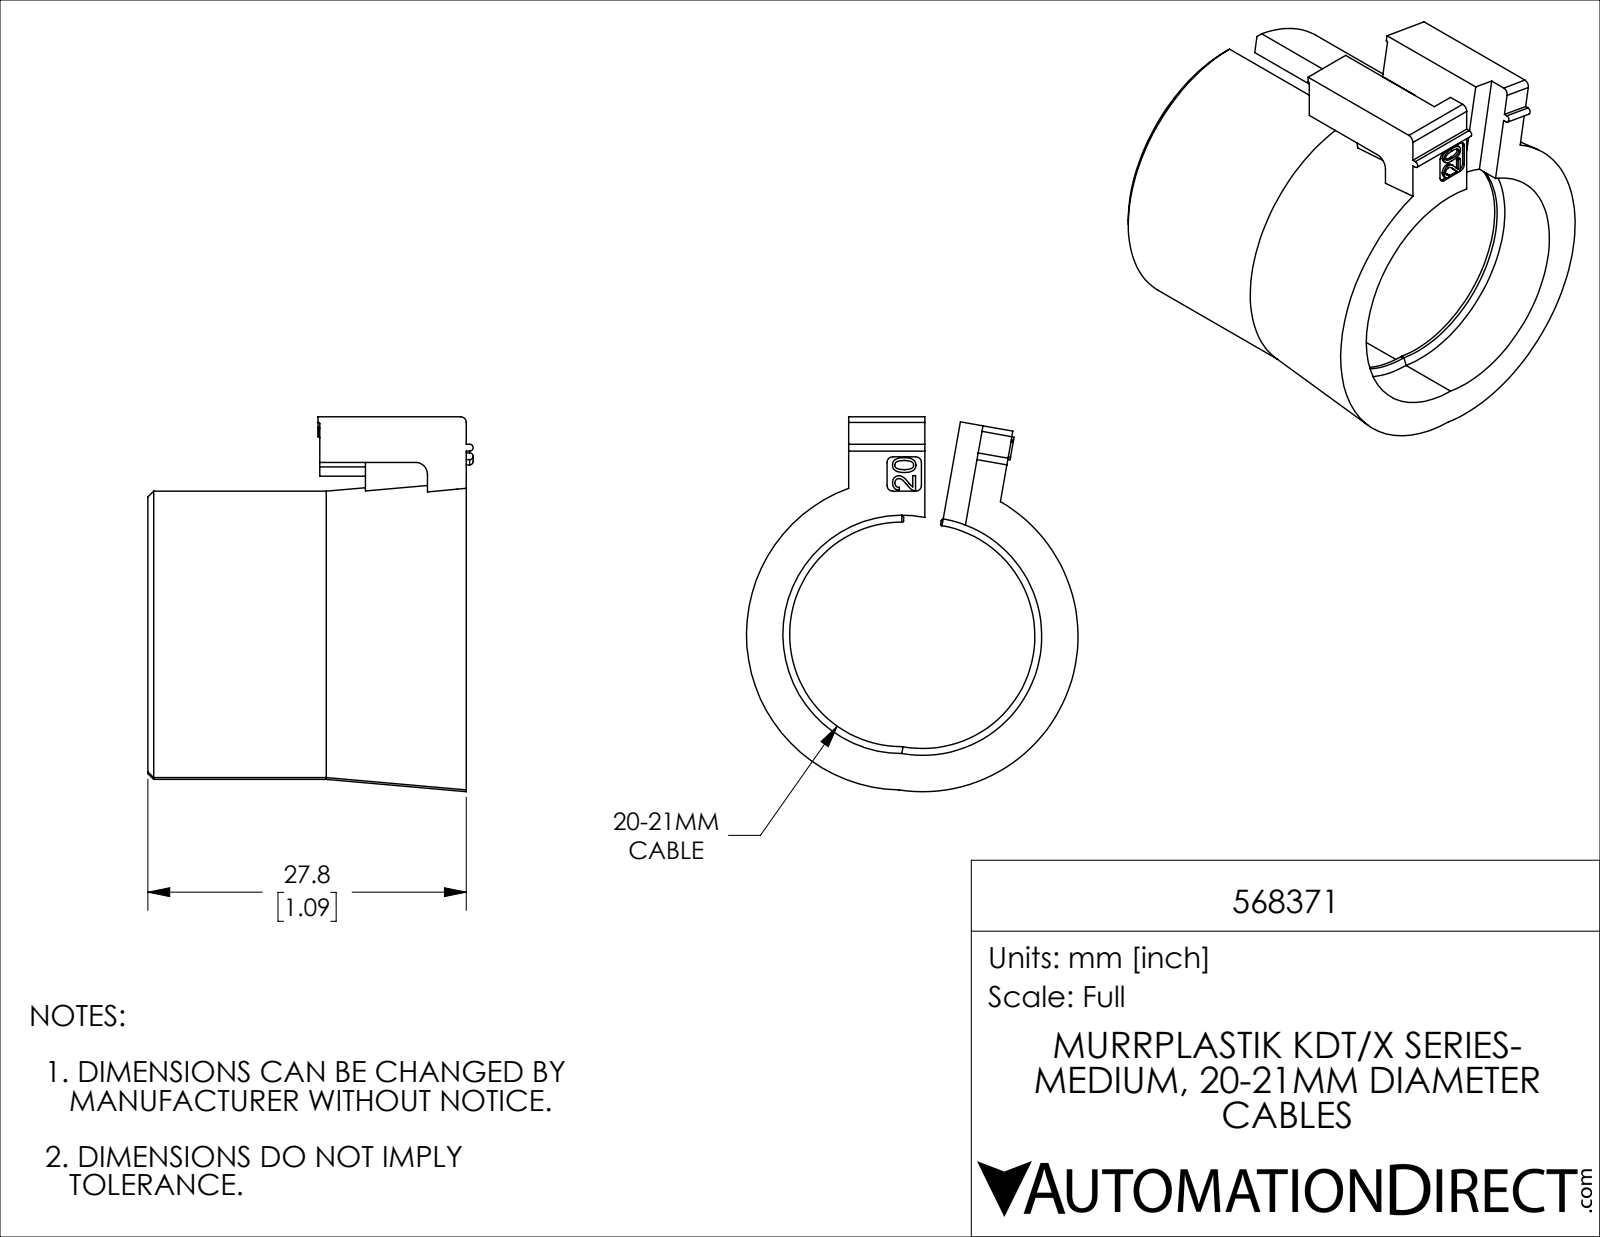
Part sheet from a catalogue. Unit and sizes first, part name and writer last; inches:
Units: inches
Overall size (bounding box): 1.289 × 1.14 × 1.118
Partial cylindrical surfaces — rounded edges, fillets, slot ends (radius × count): R0.004 ×6, R0.02 ×6, R0.012 ×2, R0.039 ×2, R0.386 ×2, R0.409 ×2, R0.492 ×2
Main face-to-face distances: 1.094, 0.157, 0.183, 0.183, 0.079, 1.016, 0.504, 0.425, 0.591, 0.262
Volume: 0.325 in³ · Surface area: 7.943 in²
Bodies: 1 solid, 123 faces (66 planar, 28 cylindrical, 29 other)
Part name (STEP PRODUCT): 568371
STEP written by: SolidWorks 2019 (CONFIG_CONTROL_DESIGN)
